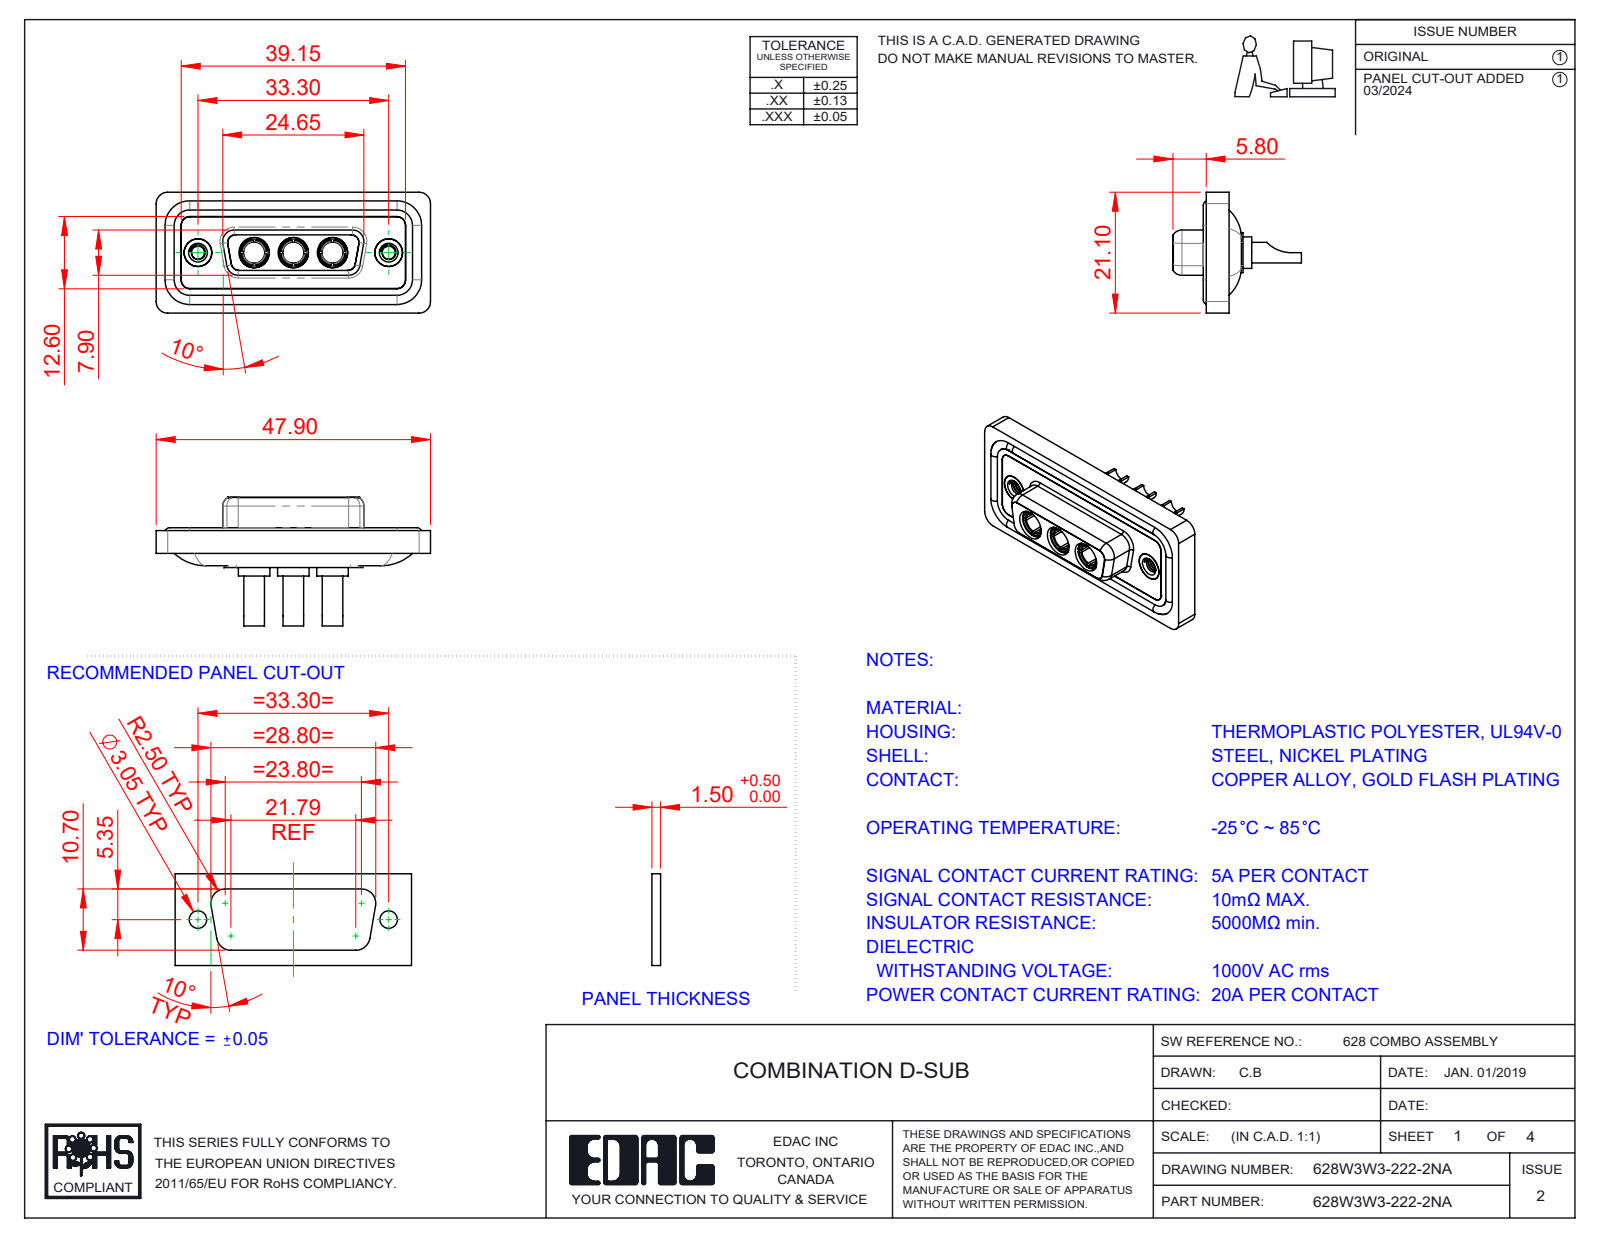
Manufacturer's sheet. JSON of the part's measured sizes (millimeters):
{"part_name": "628W3W3-222-2NA; 628Combo Waterproof Housing_15 Contacts; 628Combo Shell Rear_15 Contacts; 628Combo Shell Front_15 Contacts (+3 more)", "step_written_by": "SolidWorks 2023 (CONFIG_CONTROL_DESIGN)", "units": "millimeters", "bodies": {"solids": 13, "faces": 624, "planar": 201, "cylindrical": 268, "other": 155}, "overall_size": [47.9, 22.45, 21.1], "volume_mm3": 6066, "surface_area_mm2": 9984, "round_holes": [[4.85, 5], [2.7, 3], [3.7, 3], [5.3, 3], [2.26, 2], [4, 2], [4.05, 2], [5, 2]], "round_bosses_or_shafts": [[1.6, 4], [5.5, 3], [5.2, 3], [4.96, 3], [4.75, 3], [3.75, 3], [3.6, 3], [4.95, 2]], "partial_cylinders_radius": [[1.5, 22], [2, 20], [1.35, 12], [1.6, 8], [0.25, 4], [0.5, 4], [0.6, 4], [0.65, 4]], "face_to_face_distances": [0.4, 1.8, 1.6, 0.5, 7.45, 1.1, 2.9, 5.65, 7.05, 6.6], "hole_center_spacings": [6.85, 9.8, 16.65, 23.5, 13.7, 33.3]}
